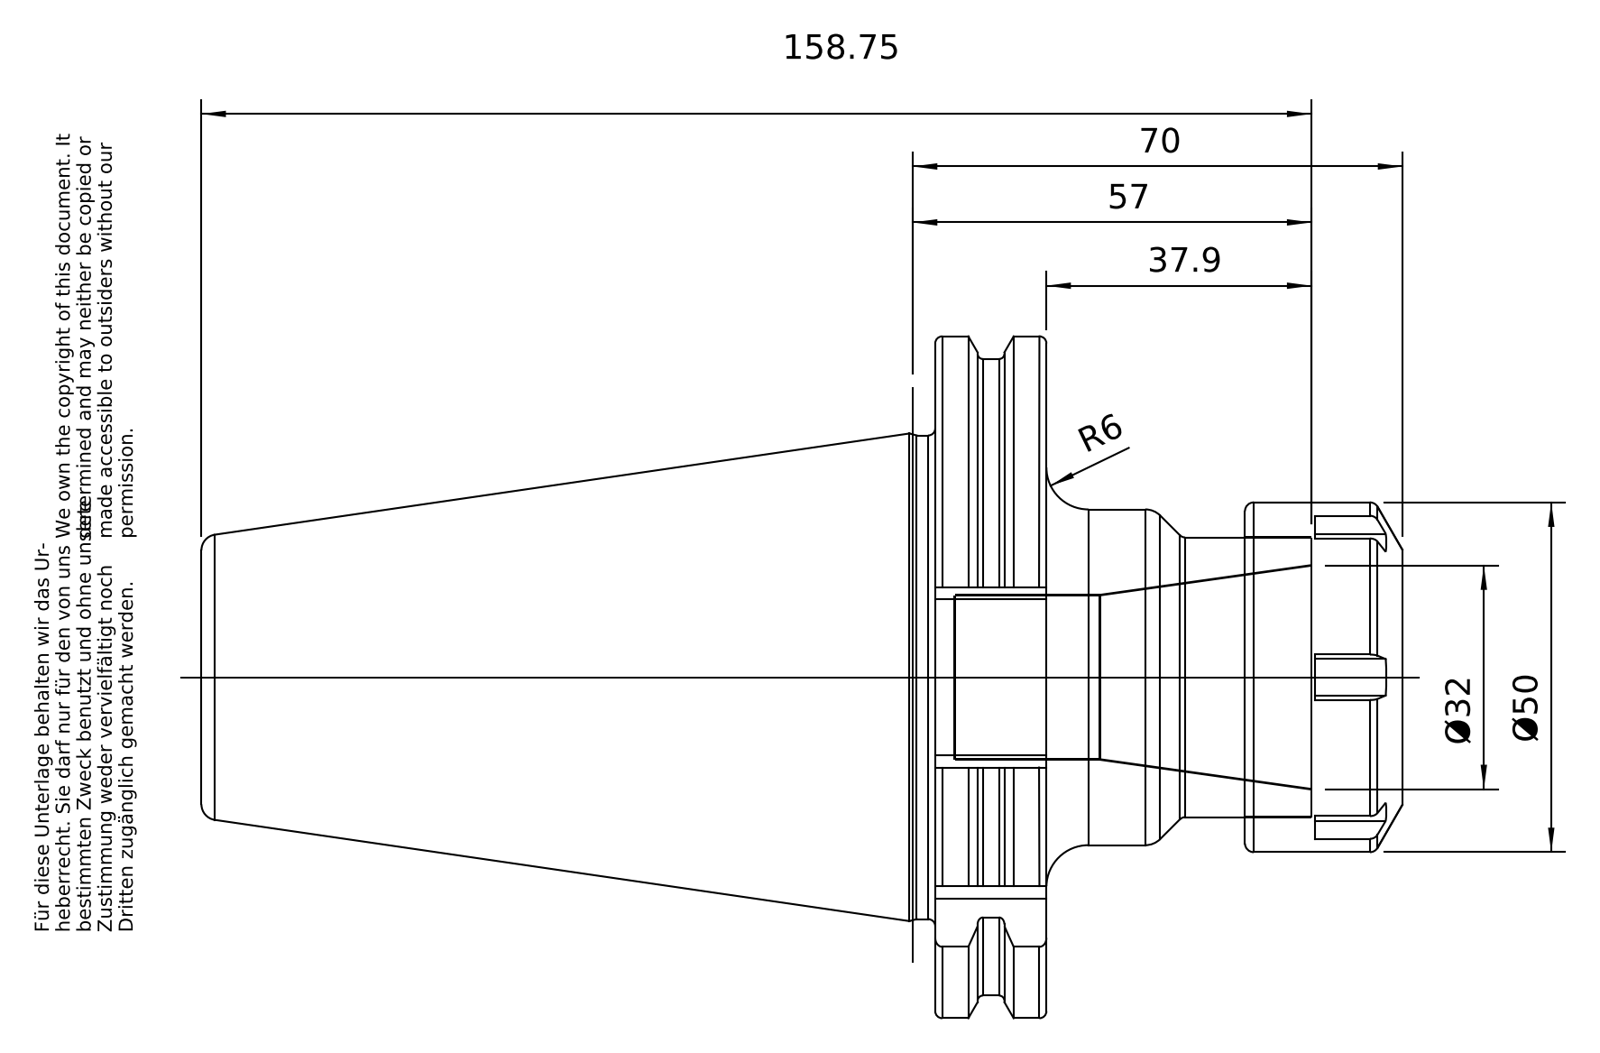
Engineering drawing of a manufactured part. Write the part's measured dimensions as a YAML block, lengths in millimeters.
part_name: "50-320-32; 83-912-32; 50-320-32_ASM"
step_written_by: "PRO/ENGINEER BY PARAMETRIC TECHNOLOGY CORPORATION, 2010430 (CONFIG_CONTROL_DESIGN)"
units: millimeters
bodies: {solids: 2, faces: 147, planar: 47, cylindrical: 38, other: 62}
overall_size: [171.6, 97.47, 94]
volume: 411088
surface_area: 58081
round_holes:
  - {diameter: 20.75, count: 1}
  - {diameter: 23.5, count: 1}
  - {diameter: 25.01, count: 1}
  - {diameter: 25.7, count: 1}
round_bosses_or_shafts:
  - {diameter: 91, count: 1}
  - {diameter: 69.15, count: 1}
  - {diameter: 50, count: 1}
  - {diameter: 48, count: 1}
  - {diameter: 40, count: 1}
  - {diameter: 24.01, count: 1}
partial_cylinders:
  - {radius: 2.7, count: 6}
  - {radius: 1.75, count: 5}
  - {radius: 48.74, count: 1}
face_to_face_distances: [15.85, 44.3, 28.45, 66.8, 50.95, 22.5, 53.8, 37.95, 9.5, 13]
